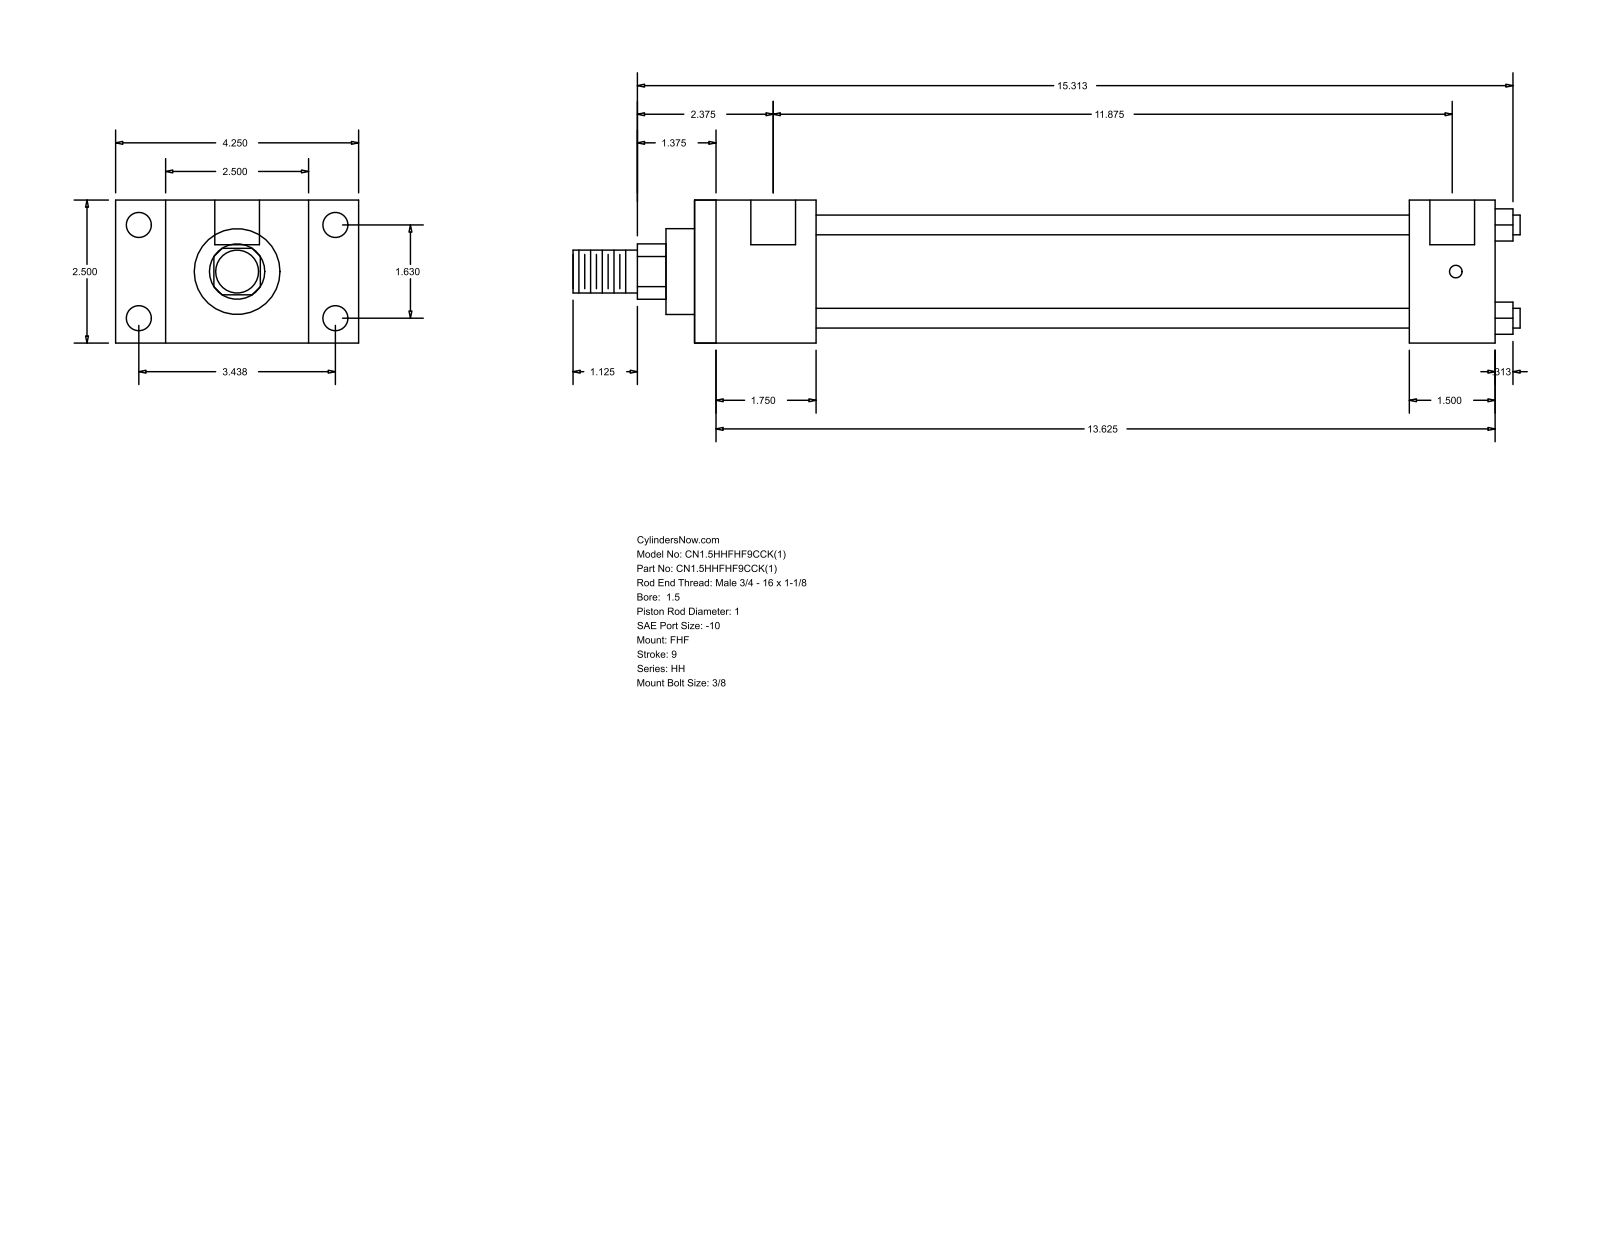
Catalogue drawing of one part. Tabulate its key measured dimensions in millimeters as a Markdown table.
| quantity | value |
| --- | --- |
| part name | HH_FHF__0150_1 |
| STEP written by | GSSL Pune (CONFIG_CONTROL_DESIGN) |
| units | millimeters |
| bodies | 0 solids, 88 faces (60 planar, 28 cylindrical, 0 other) |
| overall size | 420.69 × 107.95 × 63.5 |
| round holes (diameter × count) | 5.56 × 4, 11.13 × 4, 19.84 × 2 |
| round bosses / shafts (diameter × count) | 8.76 × 4, 44.45 × 1, 38.1 × 1, 25.4 × 1, 19.05 × 1 |
| partial cylindrical surfaces (radius × count) | 12.29 × 1 |
| main face-to-face distances | 63.5, 22.23, 85.73, 53.98, 107.96, 355.6, 301.62, 38.1, 317.5, 263.52 |
| hole center spacings | 1.59, 41.4, 87.32, 96.64, 303.21, 304.8, 301.62 |
